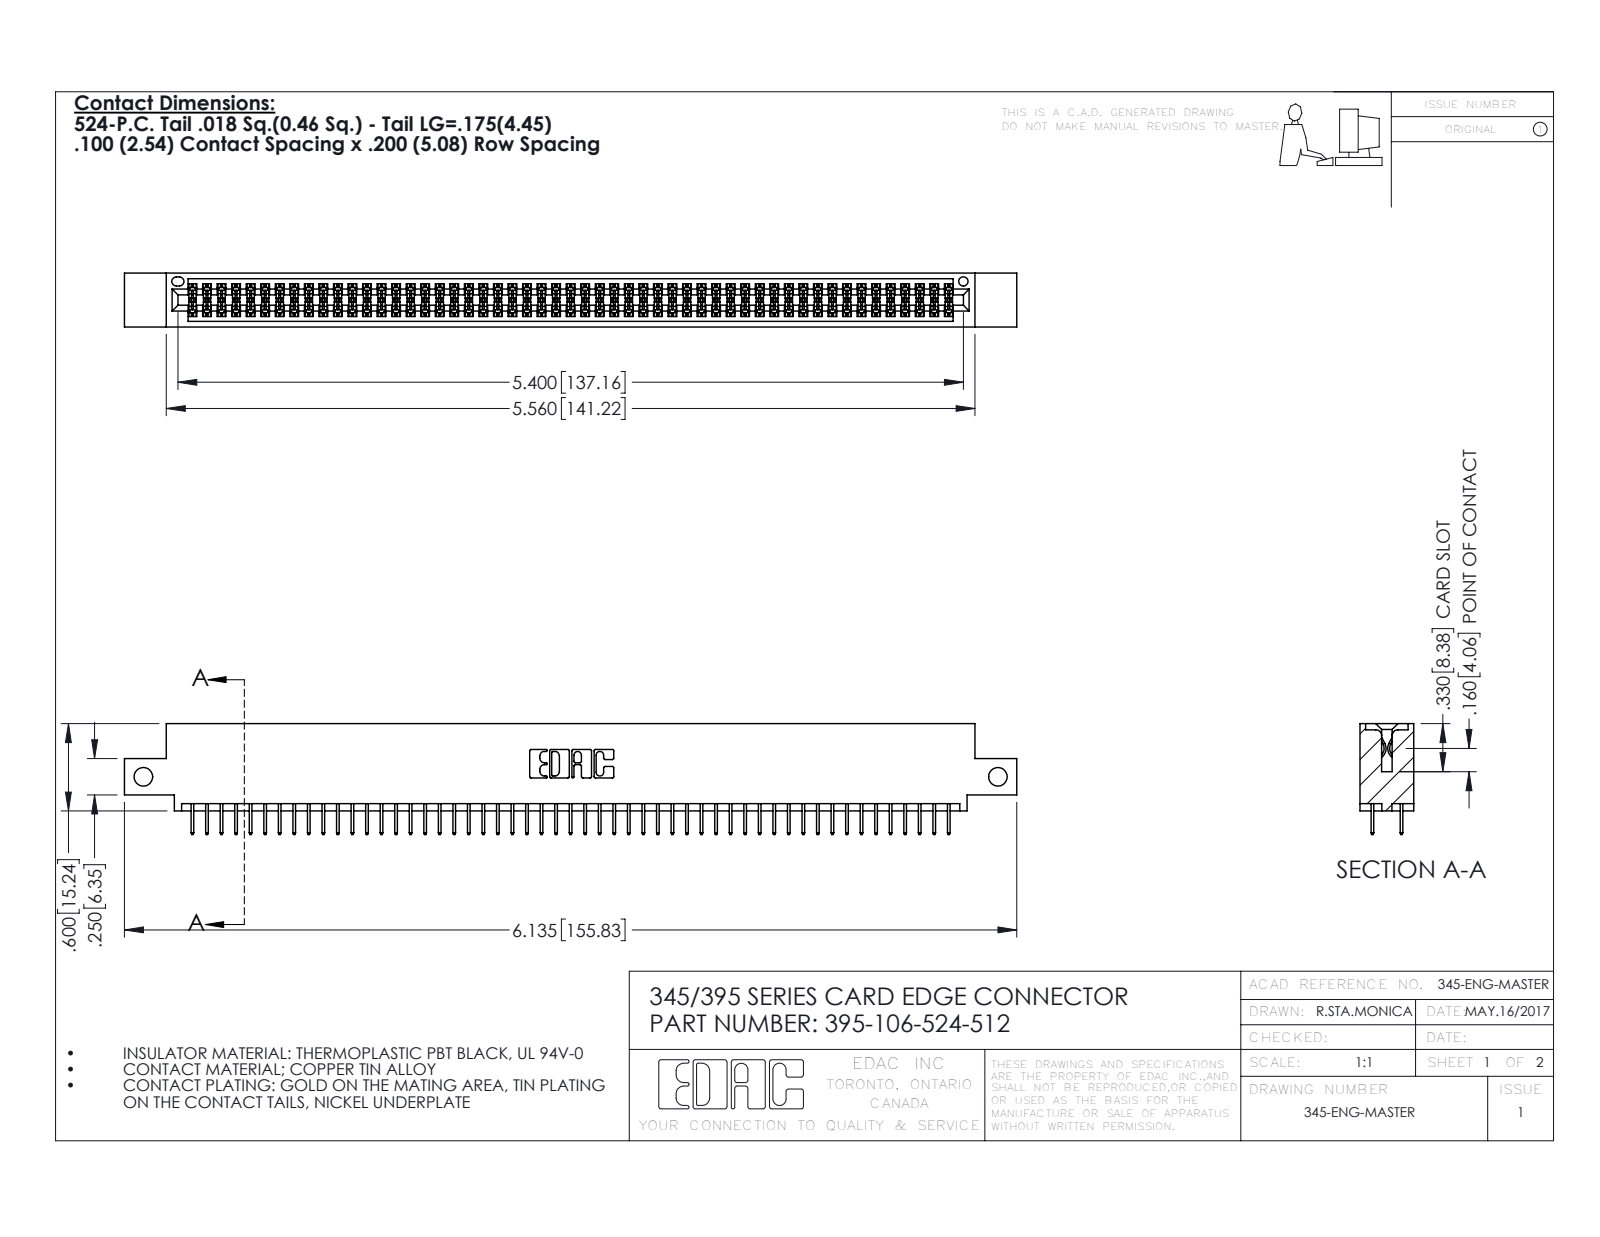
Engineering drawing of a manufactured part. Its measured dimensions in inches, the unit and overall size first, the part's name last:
Units: inches
Overall size (bounding box): 6.135 × 0.762 × 0.37
Round holes (diameter × count): ⌀0.128 ×2, ⌀0.064 ×1
Partial cylindrical surfaces — rounded edges, fillets, slot ends (radius × count): R0.006 ×159, R0.01 ×22, R0.007 ×6, R0.031 ×6, R0.026 ×3, R0.014 ×2, R0.019 ×2, R0.022 ×2
Main face-to-face distances: 0.072, 0.298, 0.2, 0.37, 0.098, 0.272, 0.025, 0.225, 0.072, 0.175
Hole centre spacings: 5.875
Volume: 0.91 in³ · Surface area: 33.79 in²
Bodies: 107 solids, 5854 faces (4218 planar, 1636 cylindrical, 0 other)
Part name (STEP PRODUCT): 345-292-001_345-293-124; 345 Part_0.110 Offset - Side Mount; 395-106-524-512
STEP written by: SolidWorks 2016 (CONFIG_CONTROL_DESIGN)
